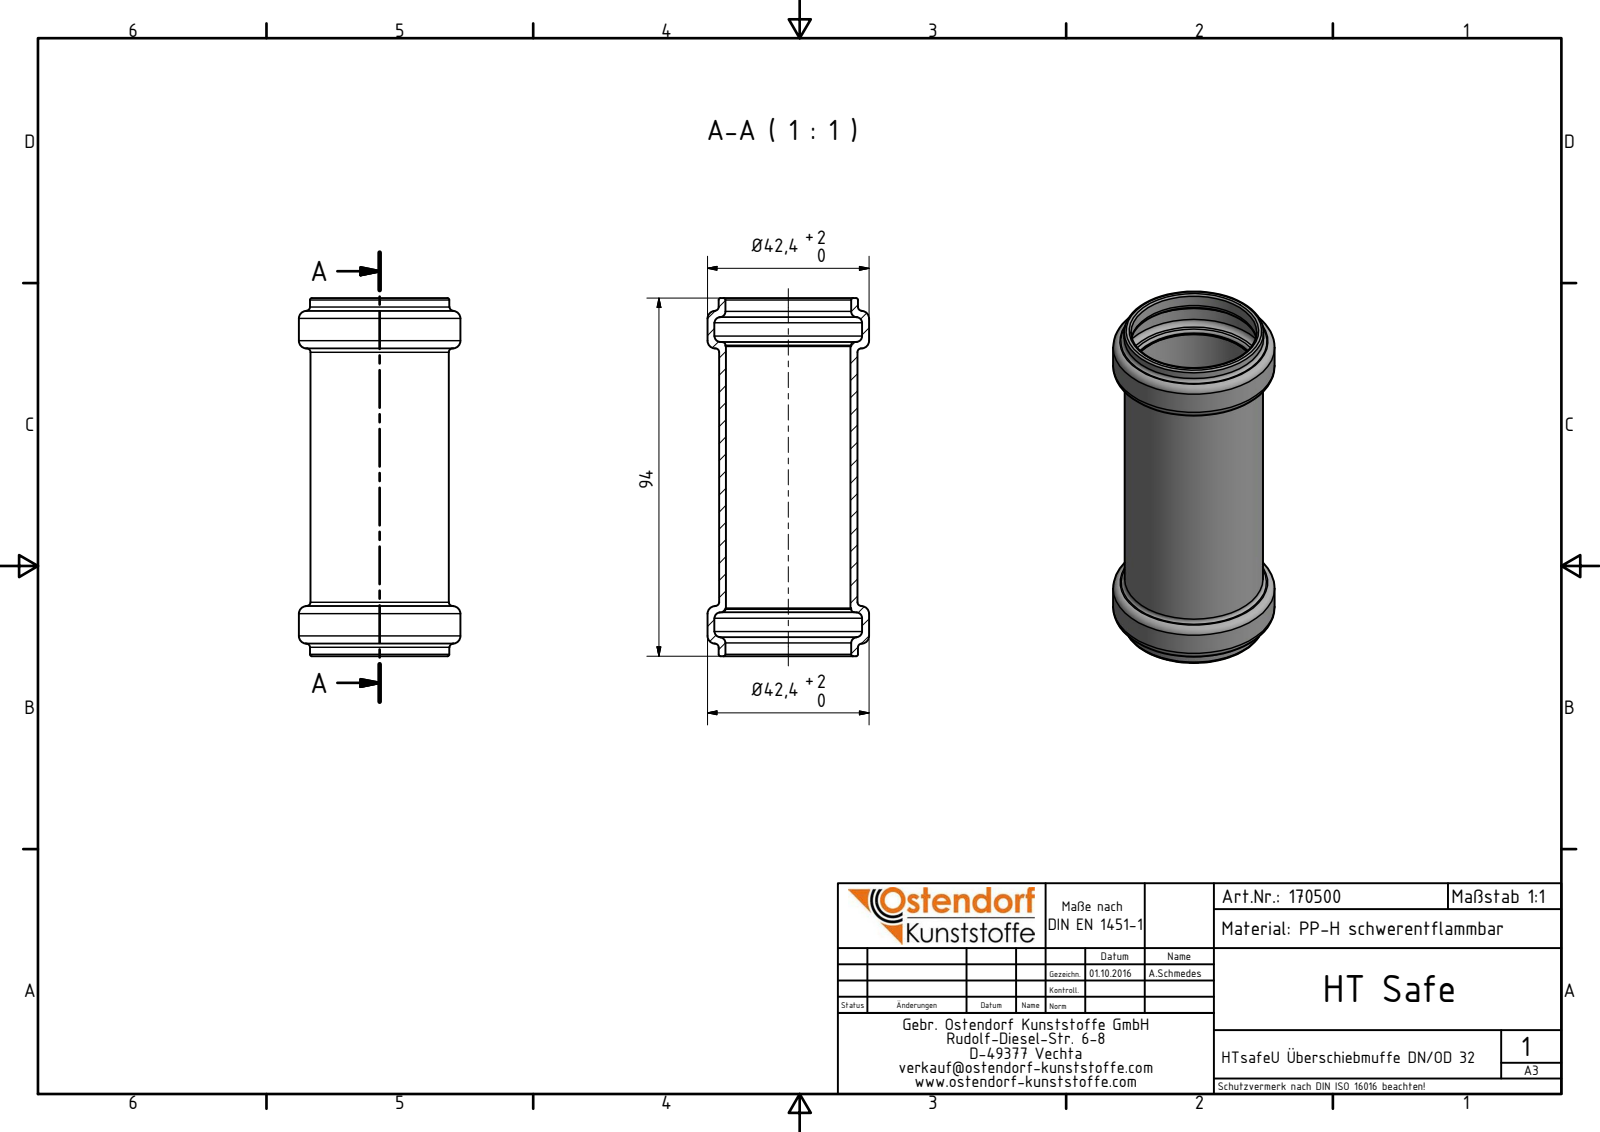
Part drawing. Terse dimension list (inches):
name: 170500 HTsafeU DN_OD 32
written by: Autodesk Inventor 2016 (AUTOMOTIVE_DESIGN)
unit: in
bodies: 1 solid, 44 faces (4 planar, 12 cylindrical, 28 other)
size: 3.701 × 1.669 × 1.669
volume: 1.278 in³; area: 35.55 in²
holes: 1× ⌀1.287, 1× ⌀1.299, 1× ⌀1.528
bosses: 1× ⌀1.669, 1× ⌀1.441, 1× ⌀1.429
face distances: 3.701, 0.497, 3.204, 2.706
